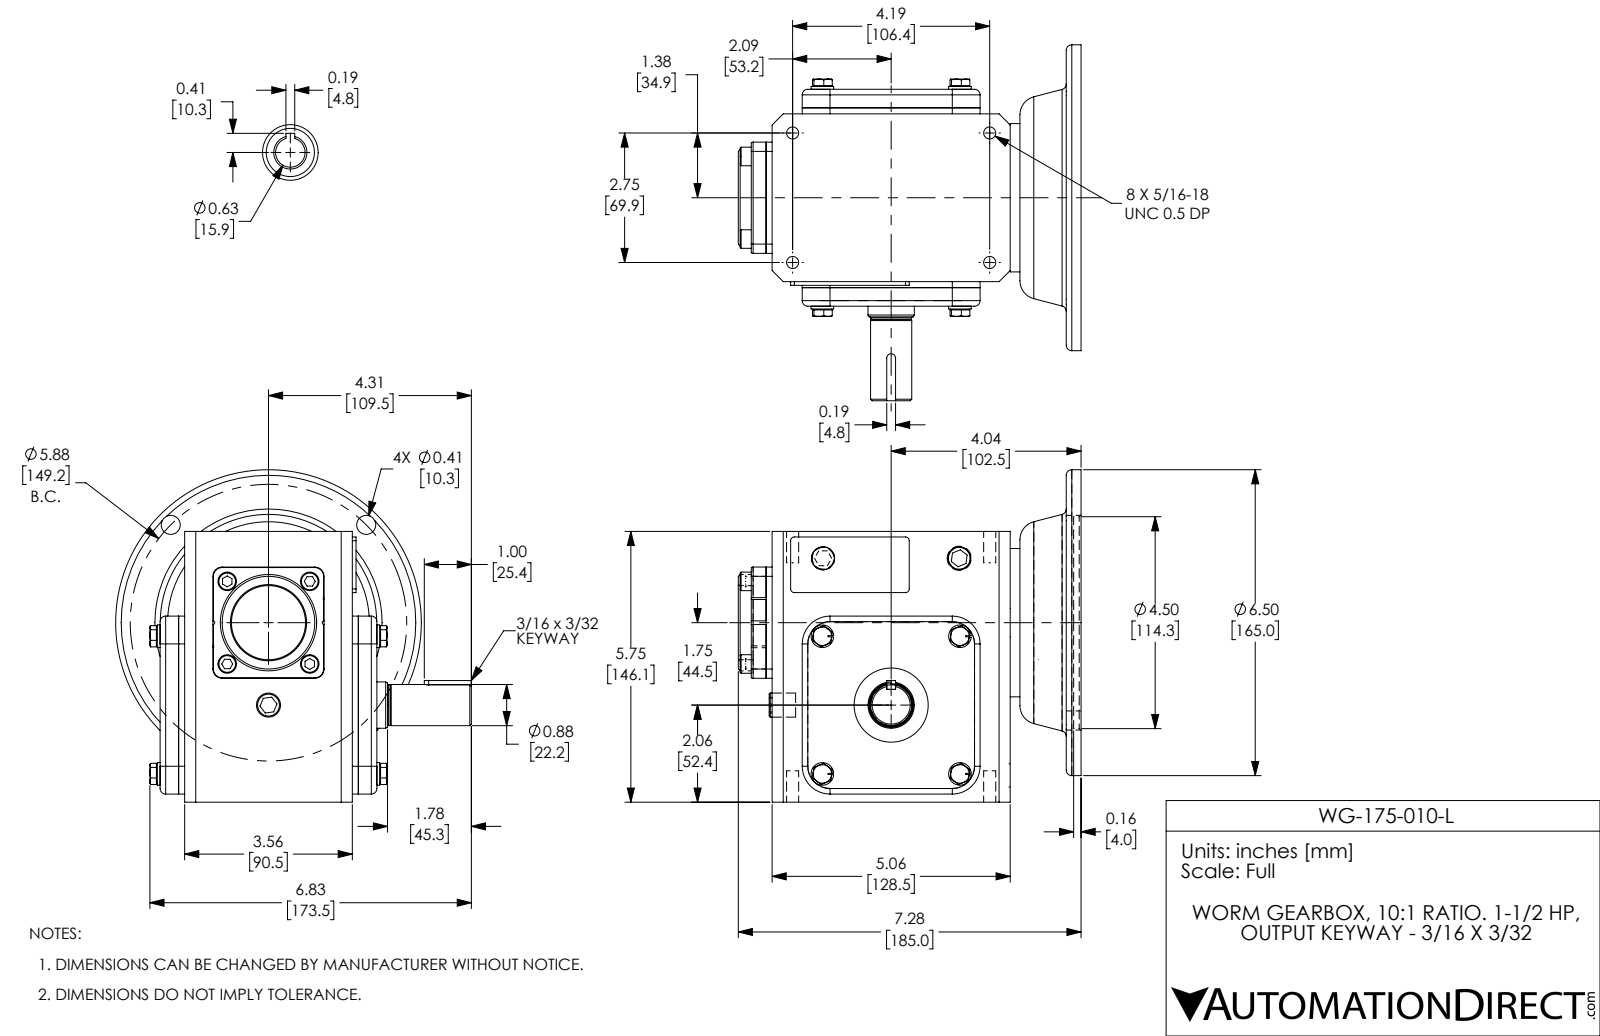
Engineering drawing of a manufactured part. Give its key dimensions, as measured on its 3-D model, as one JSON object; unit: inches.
{"part_name": "WG-175-010-L", "step_written_by": "SolidWorks 2017 (AUTOMOTIVE_DESIGN)", "units": "inches", "bodies": {"solids": 43, "faces": 613, "planar": 312, "cylindrical": 172, "other": 129}, "overall_size": [7.559, 7.283, 7.06], "volume_in3": 131.9, "surface_area_in2": 366.4, "round_holes": [[0.257, 4], [0.406, 4], [0.512, 1], [0.625, 1], [0.984, 1], [1.181, 1], [1.457, 1], [1.575, 1], [3.543, 1], [4.5, 1]], "round_bosses_or_shafts": [[0.394, 8], [0.48, 4], [0.512, 2], [6.496, 1], [3.15, 1], [2.047, 1], [1.575, 1], [0.875, 1]], "partial_cylinders_radius": [[0.079, 8], [0.118, 8], [0.197, 4], [0.591, 4], [0.02, 2], [0.039, 2], [0.094, 1]], "face_to_face_distances": [0.128, 3.819, 4.213, 0.394, 0.522, 3.691, 4.085, 0.315, 5.75, 6.693], "hole_center_spacings": [2.937, 4.154, 2.103, 2.75, 4.188, 4.354, 5.01, 5.875]}
